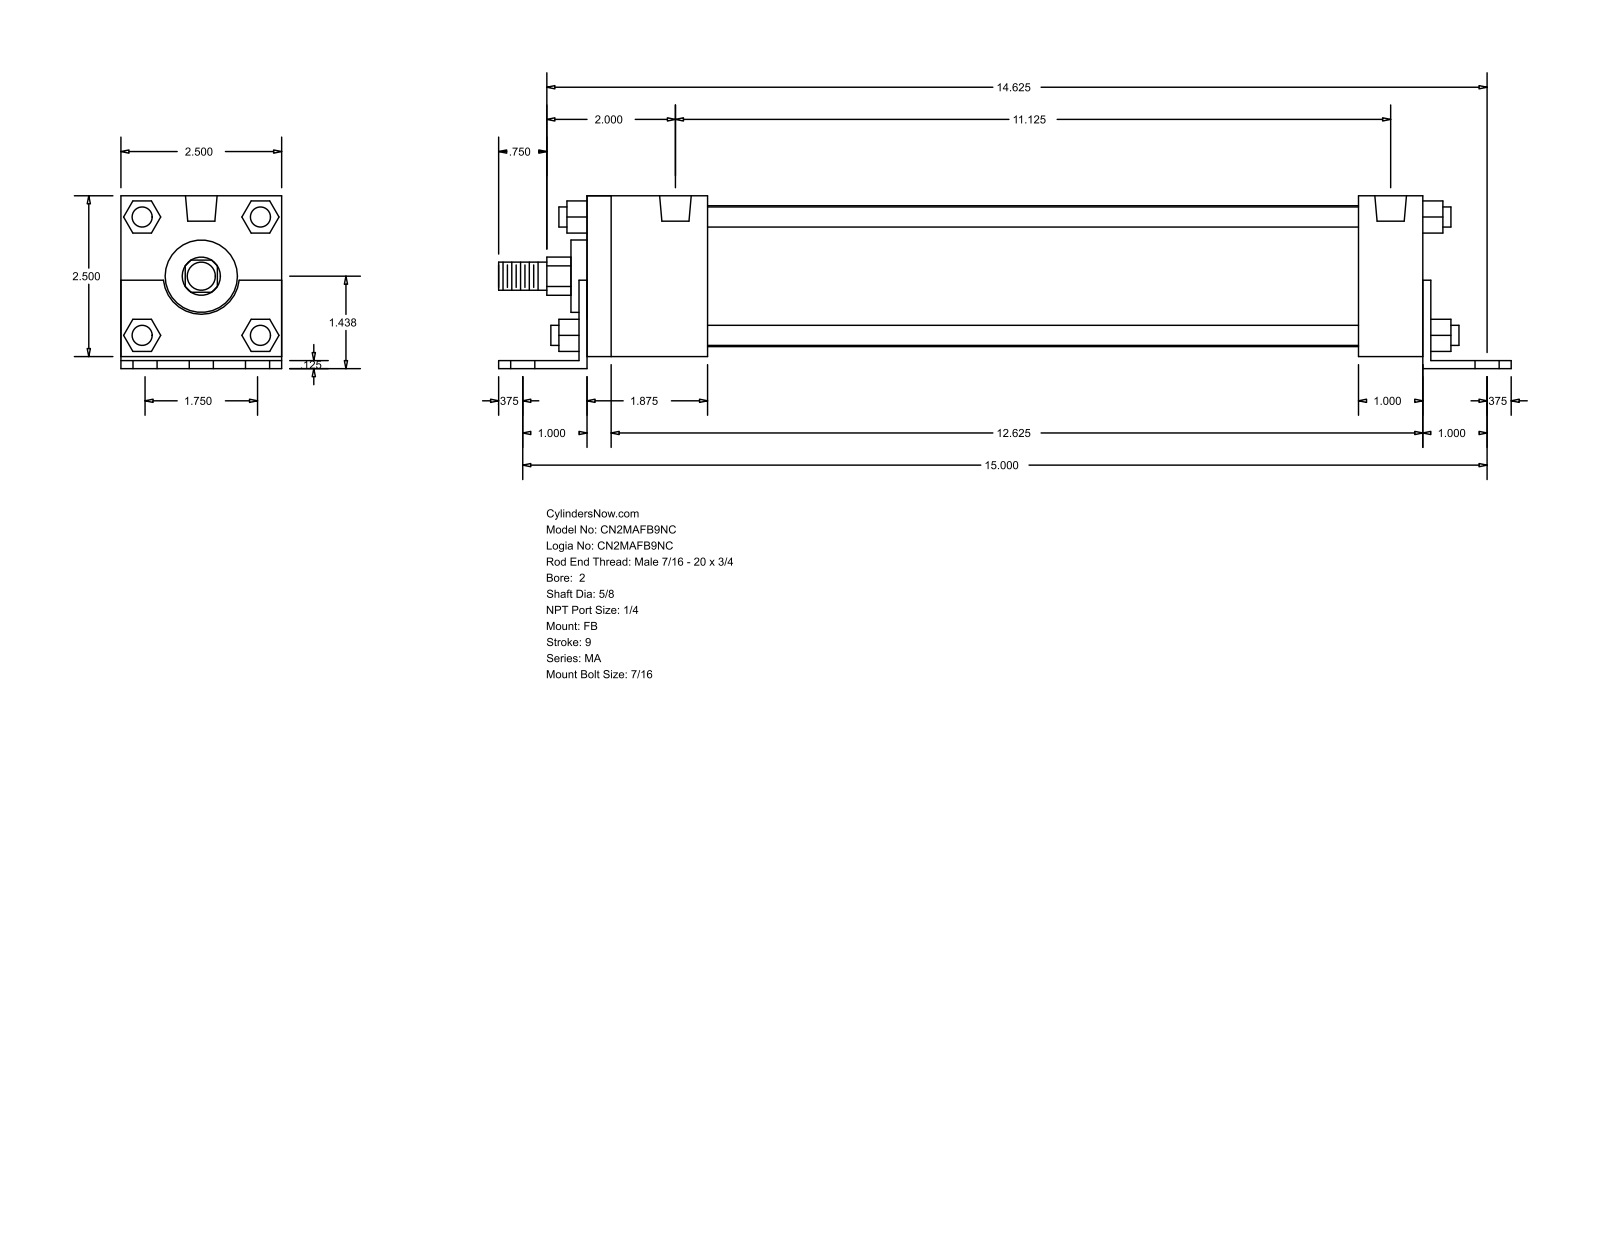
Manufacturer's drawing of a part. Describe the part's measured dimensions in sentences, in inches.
The part is named "MA_FB__0200_0.625". Its 3-D file was written by "GSSL Pune (CONFIG_CONTROL_DESIGN)". It is 0 solids with 140 faces: 105 planar, 35 cylindrical and 0 other. Overall it measures 15.75 by 2.687 by 2.5 inches. Round holes: 6 of diameter 0.437, 4 of diameter 0.313, 2 of diameter 0.492. Round bosses or shafts: 4 of diameter 0.313, 1 of diameter 2.19, 1 of diameter 1.125, 1 of diameter 0.625, 1 of diameter 0.437. Partial cylindrical surfaces (rounded edges, fillets, slot ends): 1 of radius 0.297, 1 of radius 0.593. The main face-to-face distances are 2.5, 0.187, 0.125, 2.687, 0.063, 0.125, 2.563, 13.125, 13, 0.5. The hole center spacings are 0.875, 15.026, 15, 1.737, 1.75, 2.531, 11.125, 12.656.
